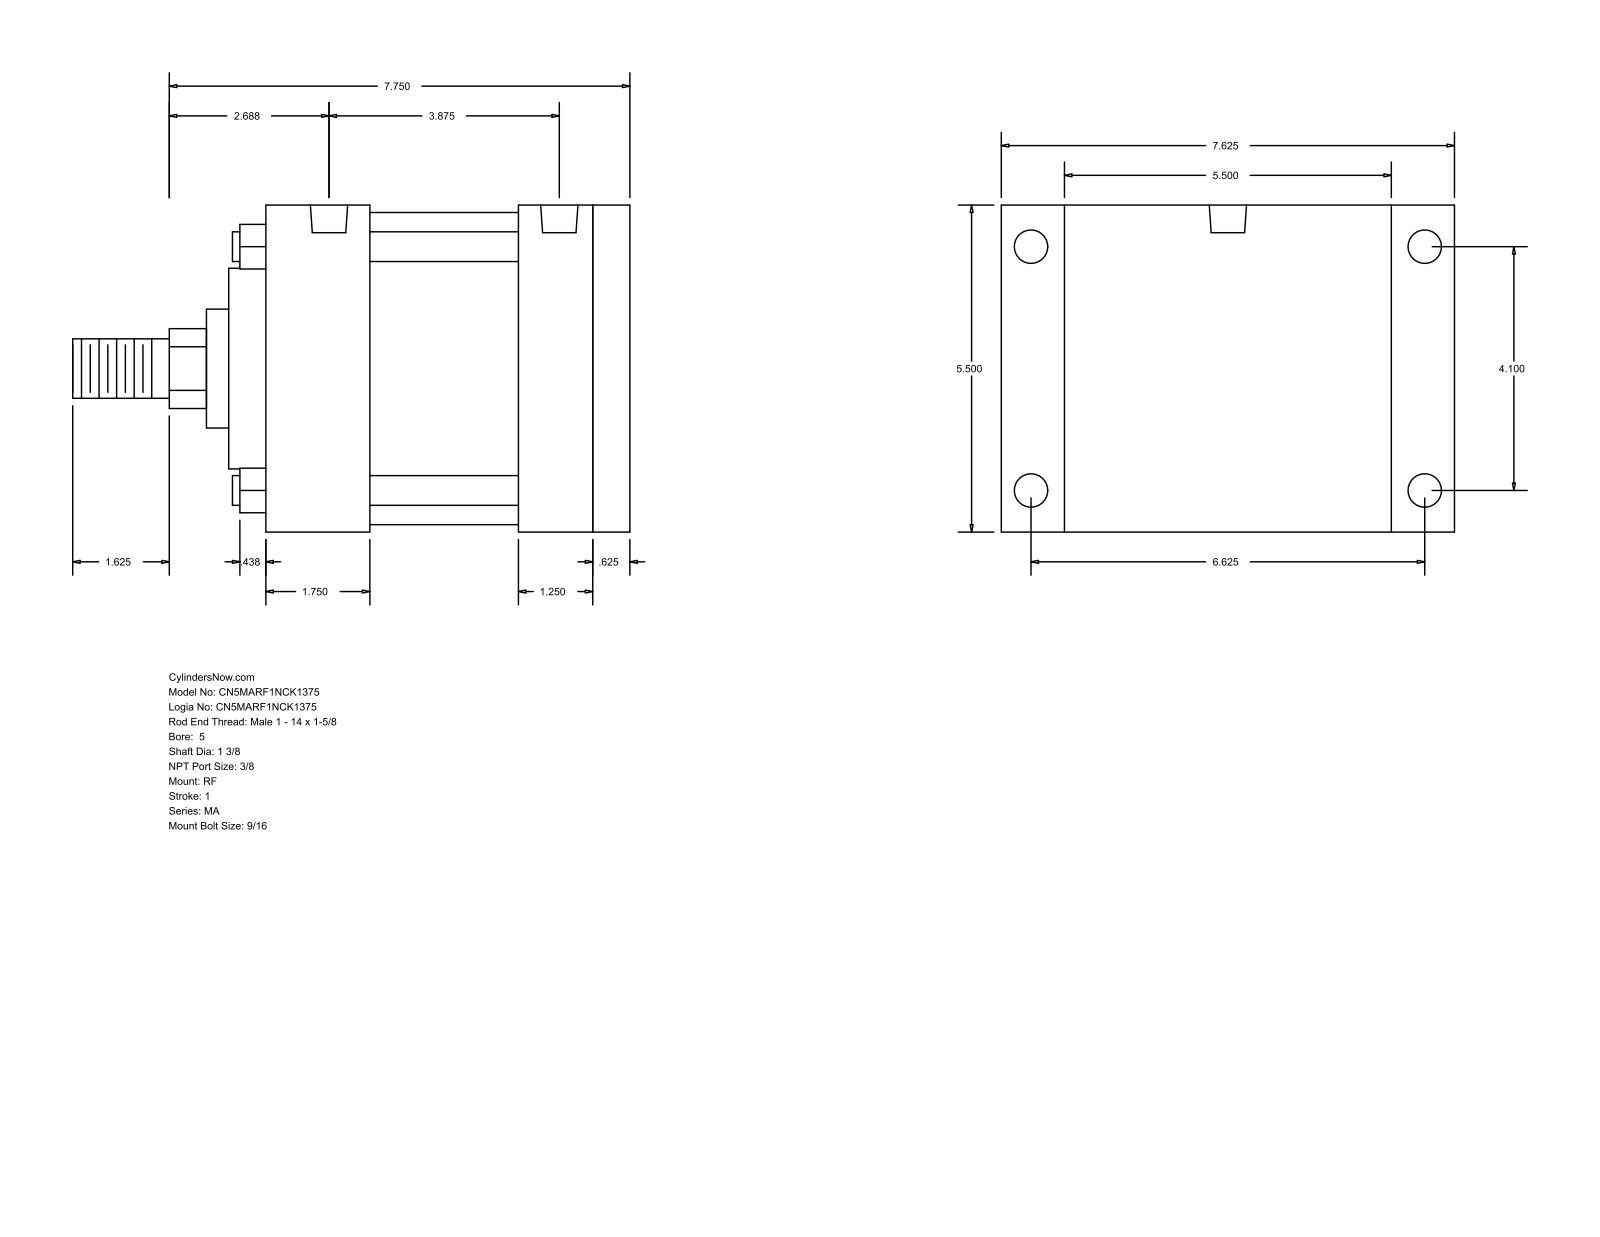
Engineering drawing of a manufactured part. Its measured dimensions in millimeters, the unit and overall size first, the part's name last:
Units: millimetres
Overall size (bounding box): 238.12 × 193.68 × 139.7
Round holes (diameter × count): ⌀11.11 ×4, ⌀14.29 ×4, ⌀15.93 ×2
Round bosses / shafts (diameter × count): ⌀12.7 ×4, ⌀133.35 ×1, ⌀85.72 ×1, ⌀50.8 ×1, ⌀34.92 ×1, ⌀25.4 ×1
Partial cylindrical surfaces — rounded edges, fillets, slot ends (radius × count): R17.06 ×1
Main face-to-face distances: 139.7, 155.58, 15.88, 111.13, 166.69, 44.45, 95.25, 107.95, 63.5, 31.75
Hole centre spacings: 88.9, 104.14, 168.28, 197.9, 4.76, 4.77, 93.66, 93.67
Bodies: 0 solids, 94 faces (65 planar, 29 cylindrical, 0 other)
Part name (STEP PRODUCT): MA_RF__0500_1.375
STEP written by: GSSL Pune (CONFIG_CONTROL_DESIGN)
